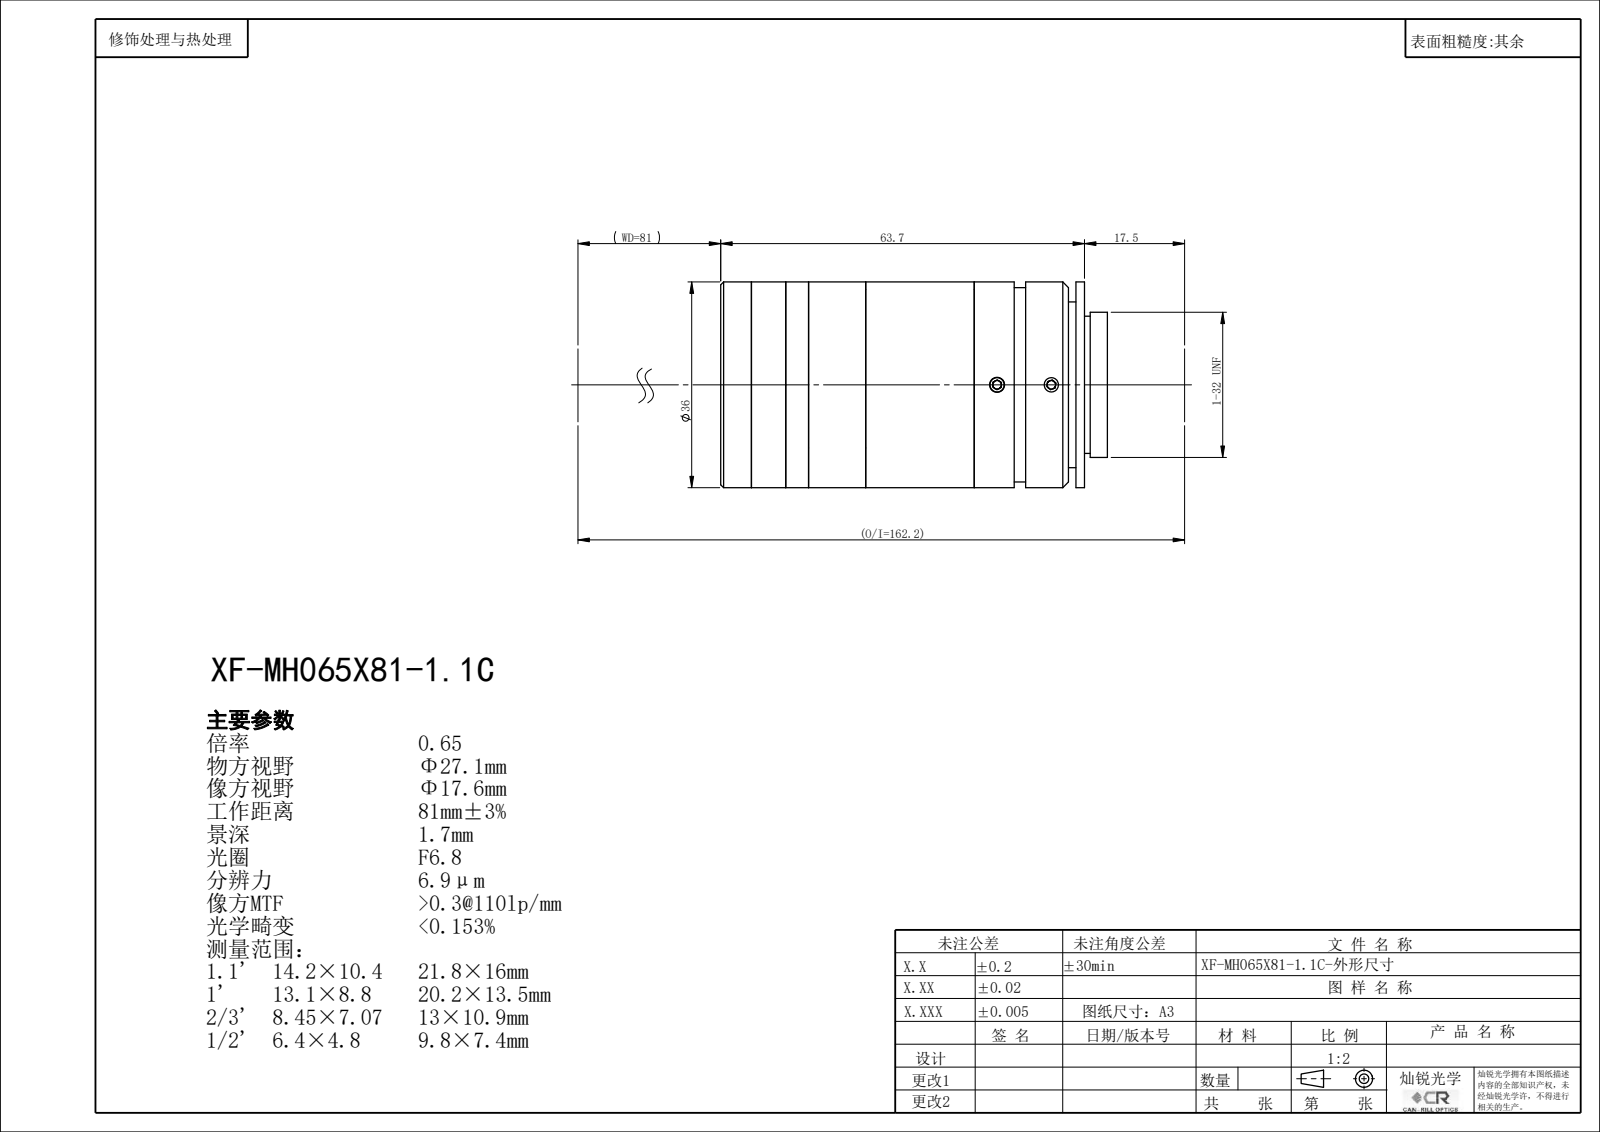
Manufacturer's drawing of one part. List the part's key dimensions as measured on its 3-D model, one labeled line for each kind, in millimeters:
Part name (STEP PRODUCT): XF-MH065X81-1.1C
STEP written by: SolidWorks 2022 (CONFIG_CONTROL_DESIGN)
Units: millimetres
Bodies: 0 solids, 138 faces (70 planar, 42 cylindrical, 26 other)
Overall size (bounding box): 67.68 × 36 × 36
Round holes (diameter × count): ⌀2.5 ×3, ⌀15 ×1, ⌀17.4 ×1, ⌀22.4 ×1, ⌀24 ×1, ⌀24.9 ×1, ⌀26 ×1, ⌀26.4 ×1
Round bosses / shafts (diameter × count): ⌀36 ×1, ⌀34 ×1, ⌀25.4 ×1
Main face-to-face distances: 19.3, 44.38, 63.68, 1.5, 62.18, 17.8, 10, 25.38, 19, 36.8
